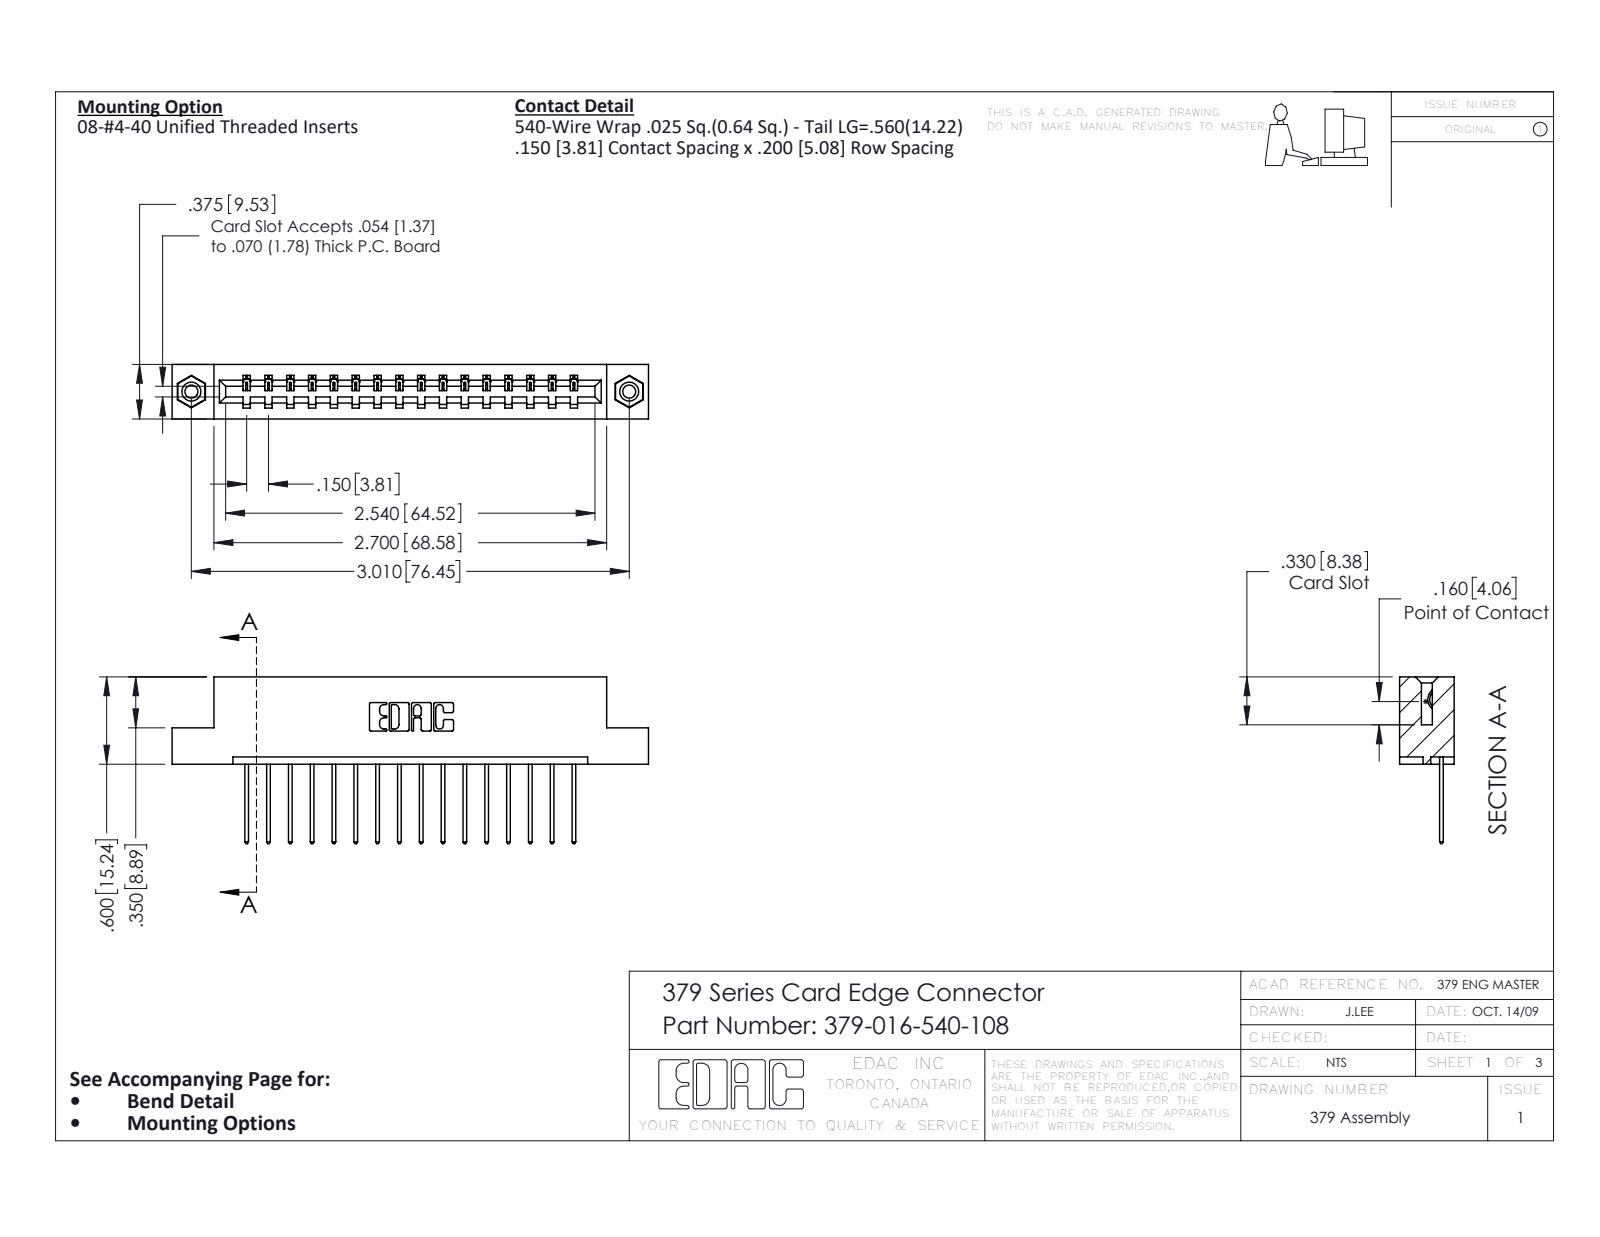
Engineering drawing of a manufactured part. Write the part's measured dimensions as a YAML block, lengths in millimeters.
part_name: "379-016-540-108; 379 Part_Flush - .156 Dia - TI; 345-292-001_345-293-140; 345-250-001_345-250-003-102"
step_written_by: "SolidWorks 2020 (CONFIG_CONTROL_DESIGN)"
units: millimeters
bodies: {solids: 19, faces: 1102, planar: 774, cylindrical: 312, other: 16}
overall_size: [83.2, 29.1, 9.5]
volume: 8440
surface_area: 8703
round_holes:
  - {diameter: 2.3, count: 2}
  - {diameter: 3.2, count: 2}
  - {diameter: 4, count: 2}
round_bosses_or_shafts:
  - {diameter: 3.9, count: 2}
partial_cylinders:
  - {radius: 0.2, count: 32}
  - {radius: 0.3, count: 32}
  - {radius: 0.3, count: 22}
  - {radius: 0.2, count: 6}
  - {radius: 0.8, count: 6}
  - {radius: 0.7, count: 3}
  - {radius: 0.4, count: 1}
  - {radius: 0.6, count: 1}
face_to_face_distances: [7.6, 1.9, 9.5, 15.2, 3.8, 5.7, 11.4, 5.1, 19.1, 7]
hole_center_spacings: [76.5]
